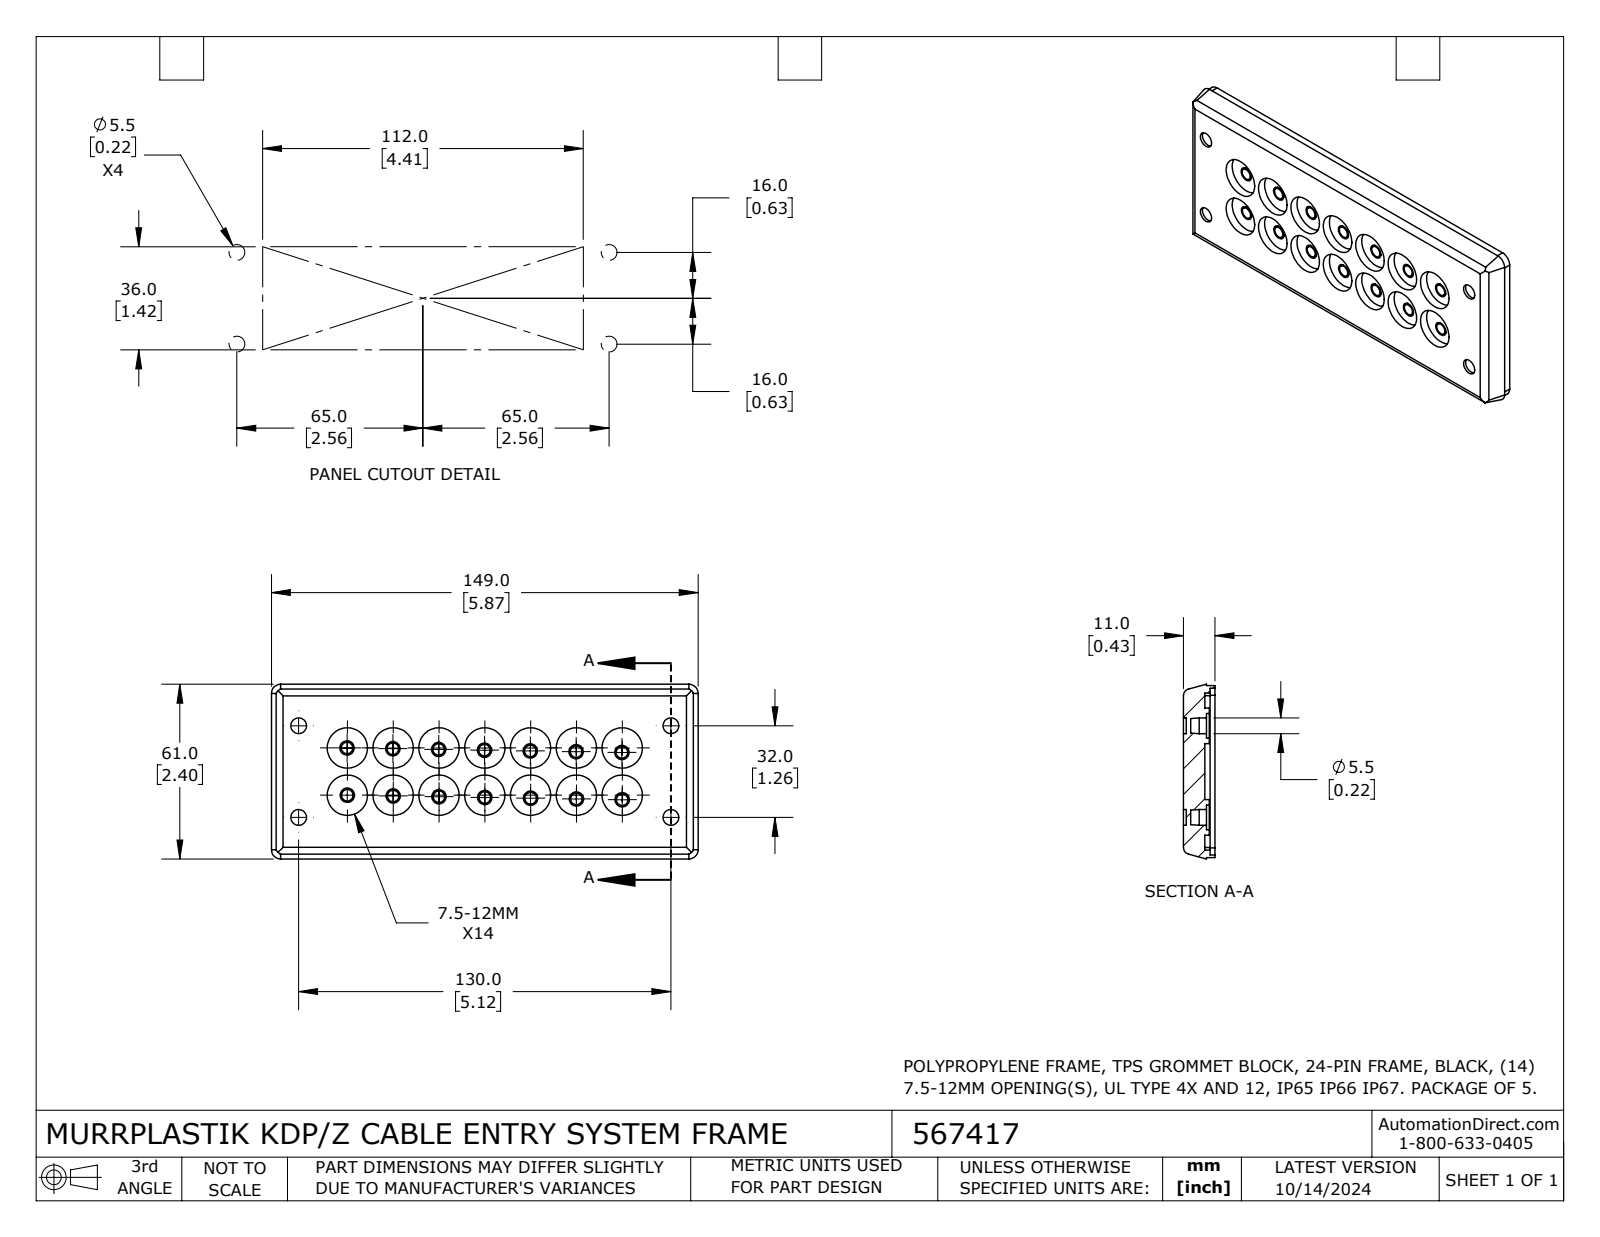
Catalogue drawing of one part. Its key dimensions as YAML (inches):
part_name: "567417"
step_written_by: "SolidWorks 2023 (CONFIG_CONTROL_DESIGN)"
units: inches
bodies: {solids: 1, faces: 259, planar: 93, cylindrical: 154, other: 12}
overall_size: [5.866, 2.402, 0.433]
volume: 2.918
surface_area: 44.67
round_holes:
  - {diameter: 0.197, count: 14}
  - {diameter: 0.554, count: 12}
  - {diameter: 0.217, count: 4}
  - {diameter: 0.339, count: 4}
  - {diameter: 0.554, count: 2}
round_bosses_or_shafts:
  - {diameter: 0.157, count: 14}
  - {diameter: 0.488, count: 4}
partial_cylinders:
  - {radius: 0.012, count: 16}
  - {radius: 0.035, count: 4}
  - {radius: 0.098, count: 4}
  - {radius: 0.098, count: 4}
  - {radius: 0.138, count: 4}
  - {radius: 0.305, count: 4}
face_to_face_distances: [0.217, 0.098, 0.118, 0.079, 0.177, 0.295, 0.067, 0.433, 0.347, 2.015]
hole_center_spacings: [0.63, 1.26, 0.65, 0.905, 1.417, 1.89, 1.89, 1.998]
